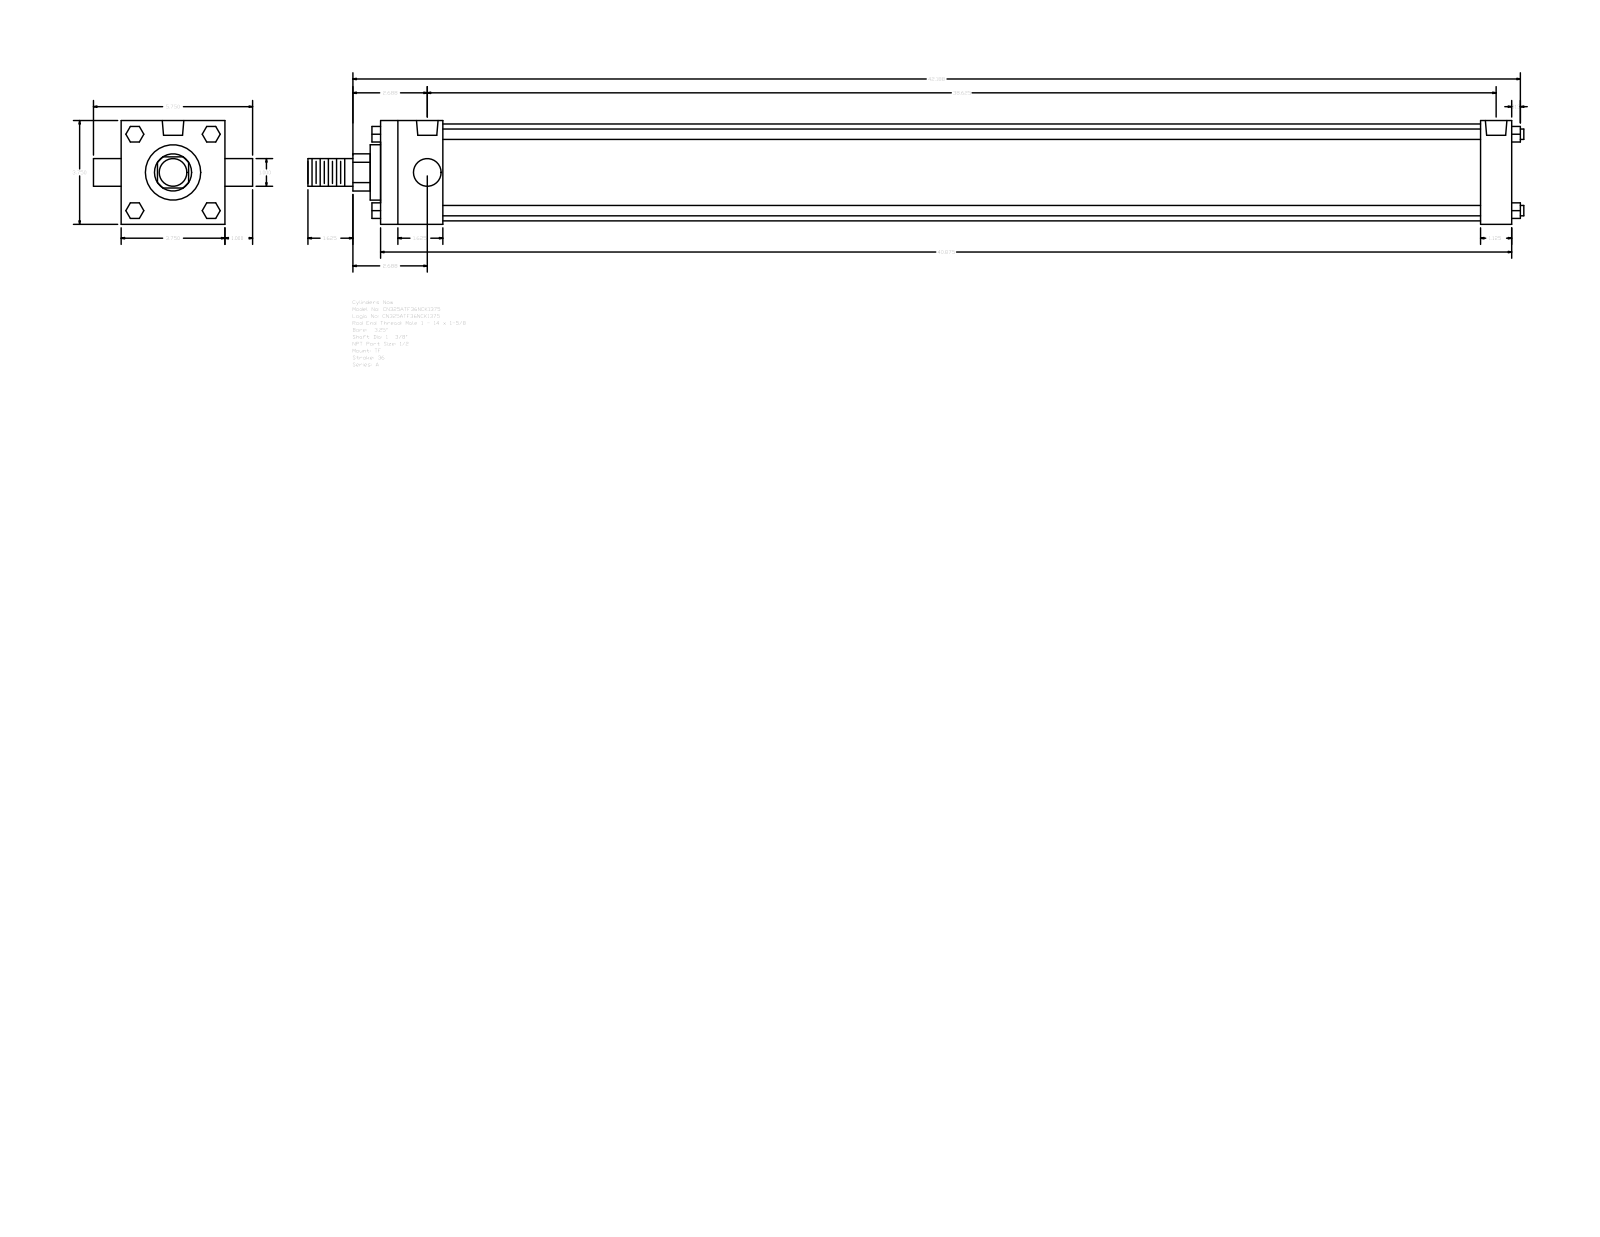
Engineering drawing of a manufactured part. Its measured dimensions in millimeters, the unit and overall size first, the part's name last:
Units: millimetres
Overall size (bounding box): 1116.01 × 146.05 × 95.25
Round holes (diameter × count): ⌀8.73 ×3, ⌀19.77 ×2
Round bosses / shafts (diameter × count): ⌀9.53 ×4, ⌀25.4 ×2, ⌀88.9 ×1, ⌀50.8 ×1, ⌀34.92 ×1
Partial cylindrical surfaces — rounded edges, fillets, slot ends (radius × count): R17.06 ×1
Main face-to-face distances: 95.24, 1038.22, 57.15, 1009.65, 952.5, 981.07, 28.57, 66.67, 9.52, 1019.17
Hole centre spacings: 3.18, 977.9, 974.72, 981.08
Bodies: 0 solids, 120 faces (92 planar, 28 cylindrical, 0 other)
Part name (STEP PRODUCT): A_TF__0325_1.375
STEP written by: GSSL Pune (CONFIG_CONTROL_DESIGN)
